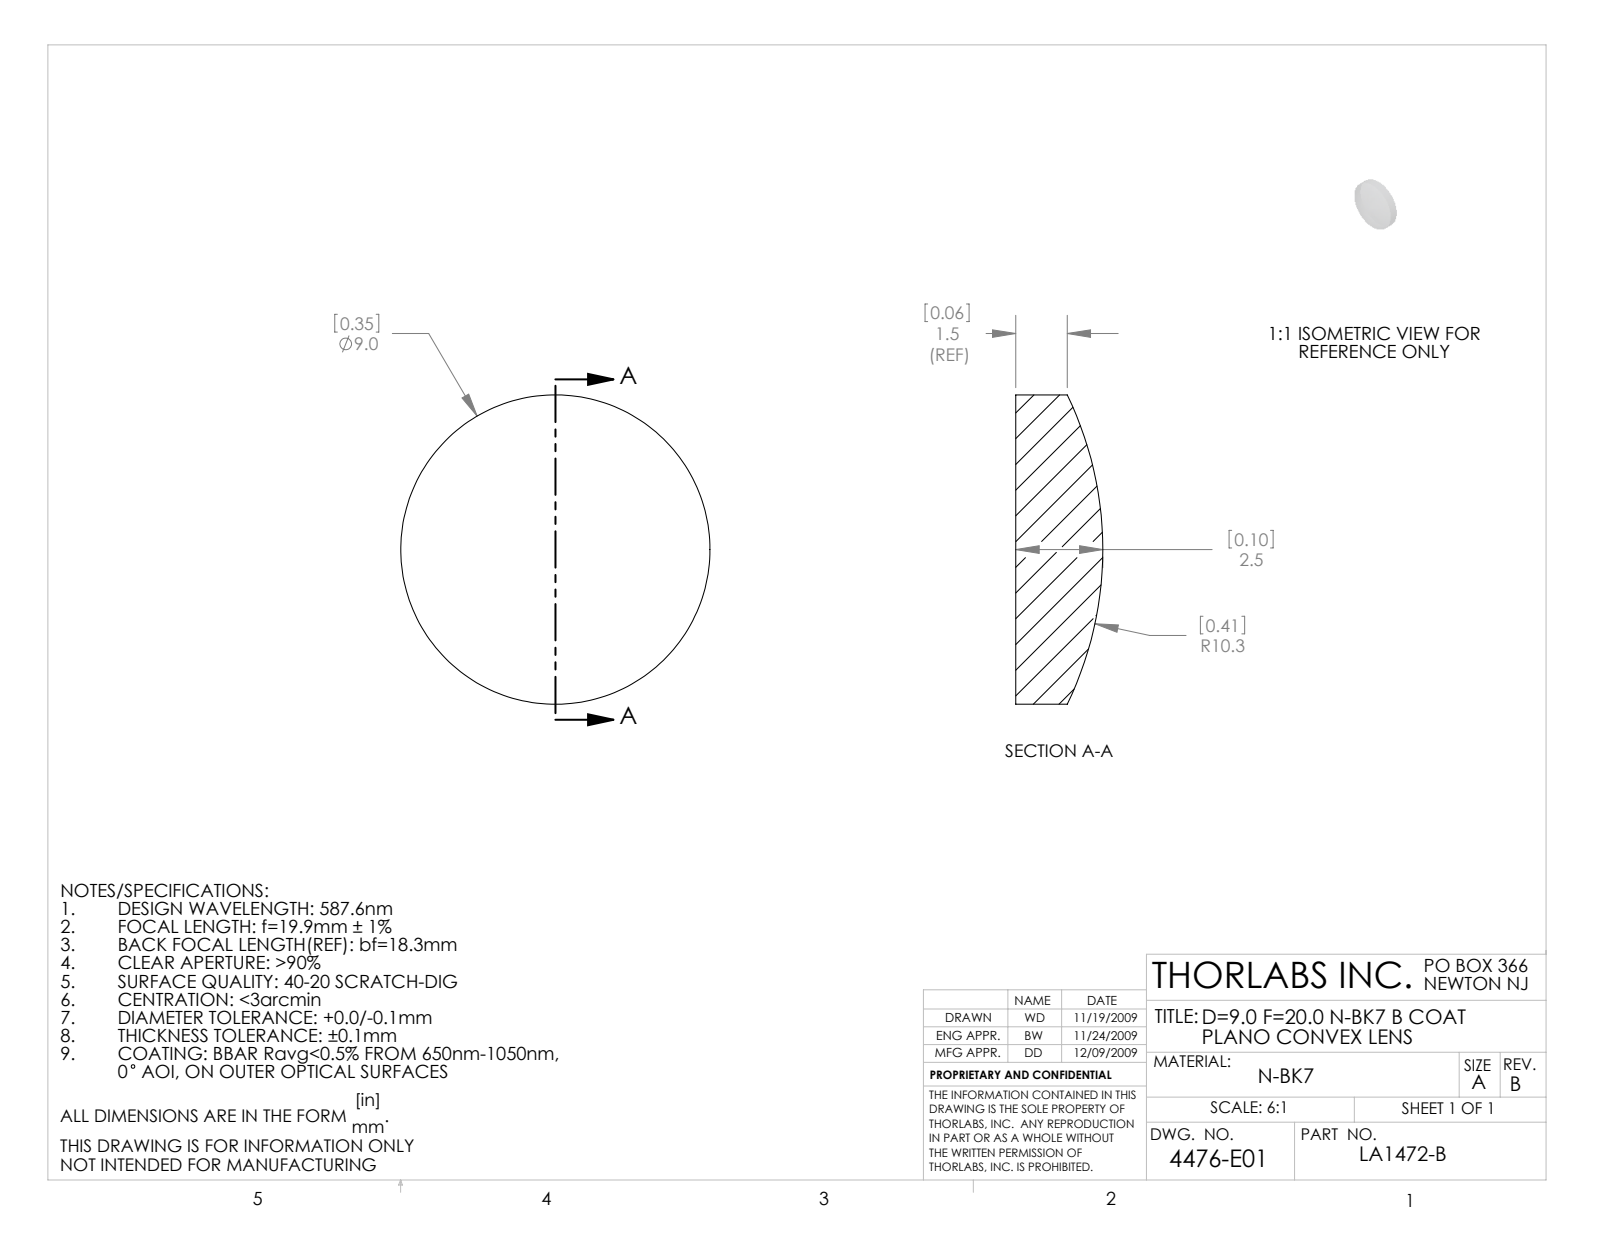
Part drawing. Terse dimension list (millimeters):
name: 4476-E0W
written by: SolidWorks 2009 (AUTOMOTIVE_DESIGN)
unit: mm
bodies: 1 solid, 5 faces (1 planar, 2 cylindrical, 2 other)
size: 9 × 9 × 2.53
volume: 129 mm³; area: 173 mm²
bosses: 1× ⌀9
